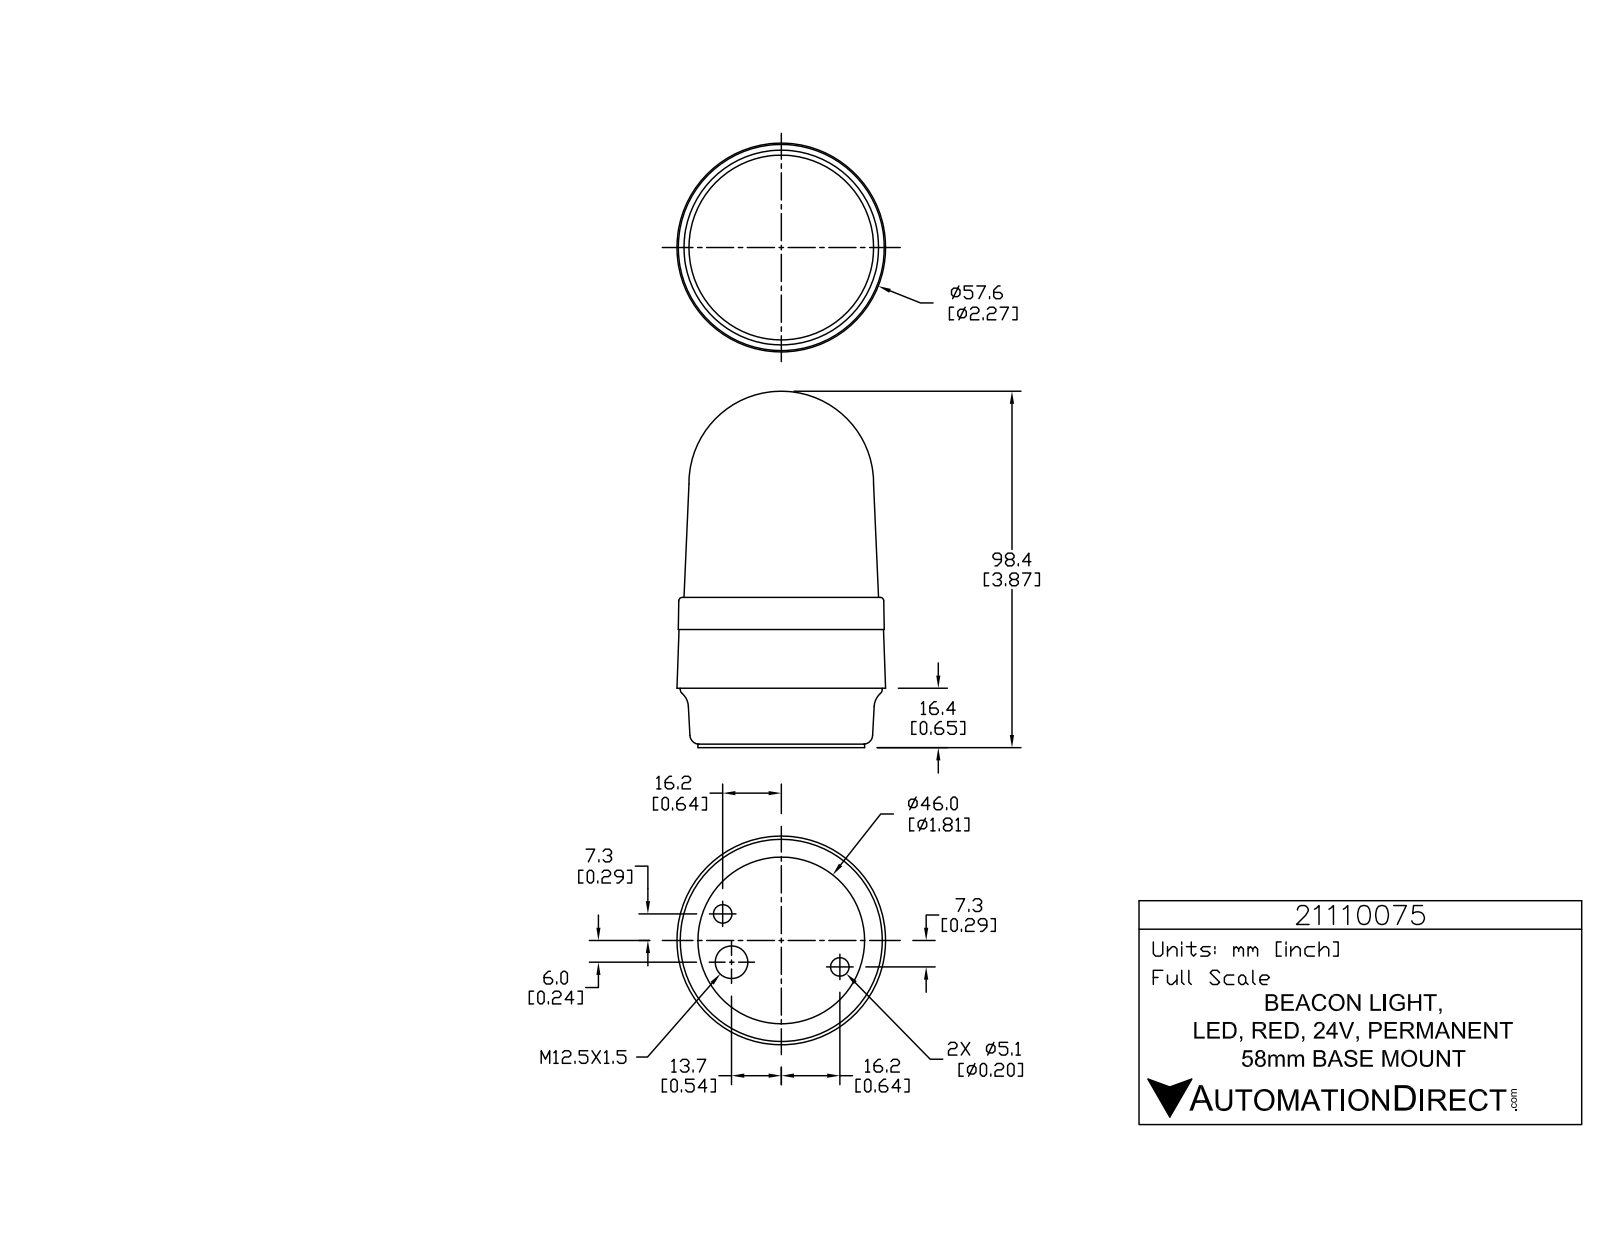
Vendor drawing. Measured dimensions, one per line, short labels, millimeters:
name: 21110075
written by: SolidWorks 2015 (AUTOMOTIVE_DESIGN)
unit: mm
bodies: 1 solid, 764 faces (527 planar, 145 cylindrical, 92 other)
size: 98.4 × 57.63 × 57.63
volume: 199 898 mm³; area: 18 922 mm²
holes: 3× ⌀0.99, 2× ⌀5.11, 1× ⌀9
bosses: 3× ⌀5.74, 3× ⌀1.43, 1× ⌀55.8, 1× ⌀46
rounds: 6× R0.2, 6× R0.21, 6× R0.21, 6× R3.32, 3× R0.1, 3× R0.12, 3× R0.19, 3× R0.2
face distances: 16.4, 1, 15.4, 41.5, 40.5, 25.1, 32.6, 31.6, 16.2, 8.9
hole spacings: 13.56, 29.94, 35.5
